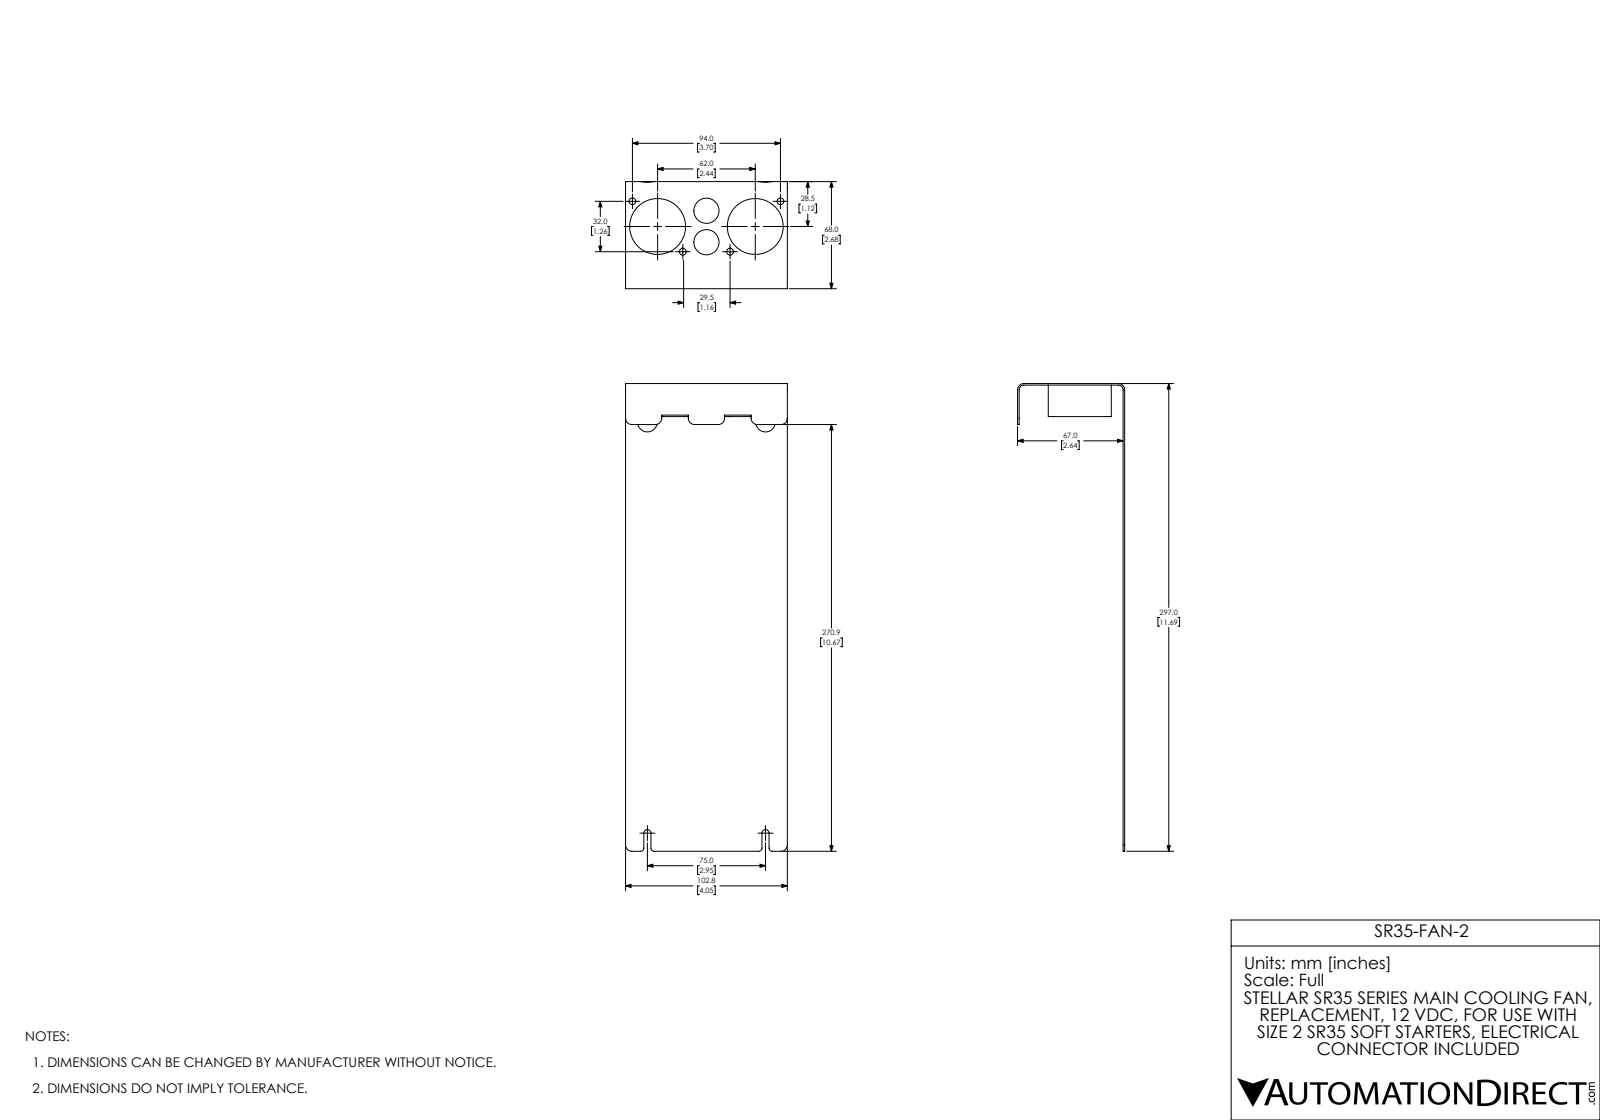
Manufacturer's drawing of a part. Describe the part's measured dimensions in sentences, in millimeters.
The part is named "STP-AGY-005-V01 (AGY2 FAN) Coord fXT". Its 3-D file was written by "SolidWorks 2017 (AUTOMOTIVE_DESIGN)". It is 3 solids with 110 faces: 42 planar, 68 cylindrical and 0 other. Overall it measures 297 by 102.7 by 68 millimeters. Its volume is 86 440 cubic millimeters and its surface area 89 610 square millimeters. Round holes: 8 of diameter 4.3, 2 of diameter 16, 2 of diameter 35.5, 2 of diameter 37.5. Partial cylindrical surfaces (rounded edges, fillets, slot ends): 10 of radius 4, 8 of radius 3.5, 4 of radius 2, 4 of radius 6.2, 2 of radius 2.3, 2 of radius 3. The main face-to-face distances are 1, 67, 20, 21, 40, 6, 15, 5, 66, 68. The hole center spacings are 22.6, 32, 62, 16.2, 30, 32.6, 45.2, 47.4.
